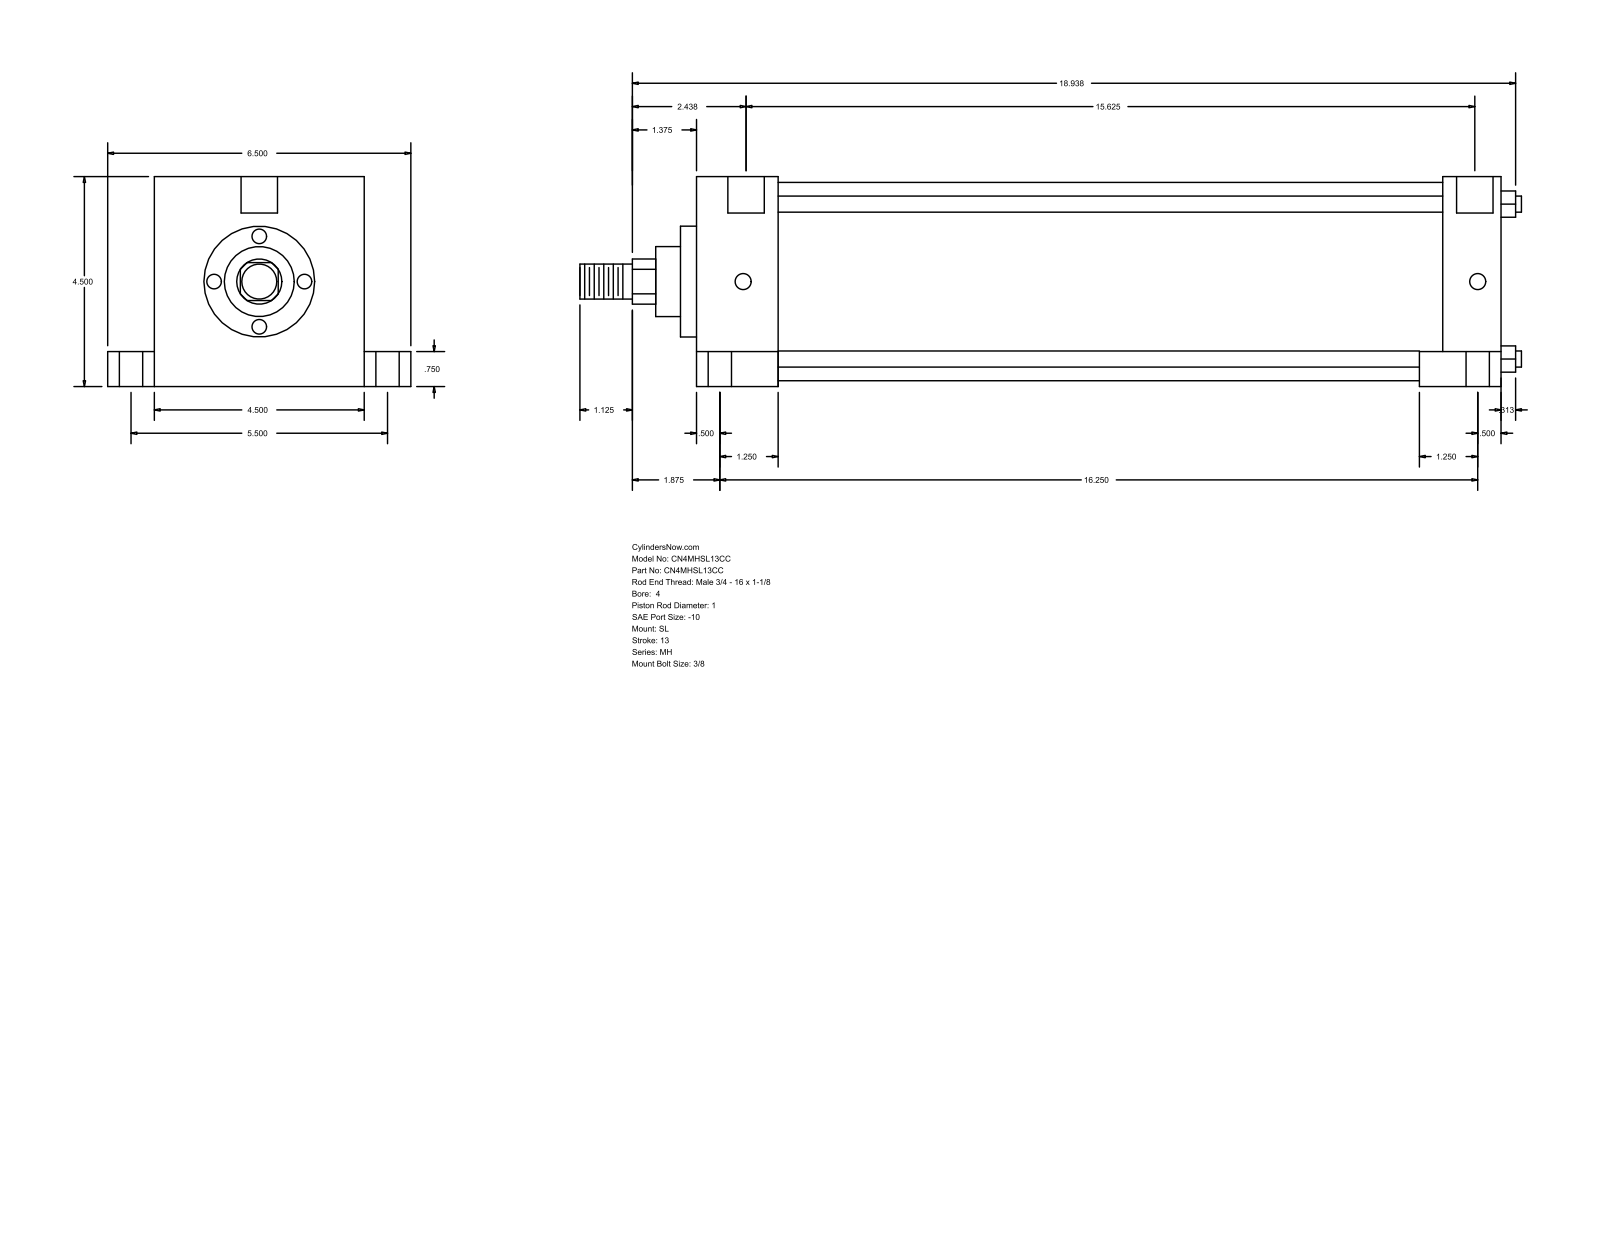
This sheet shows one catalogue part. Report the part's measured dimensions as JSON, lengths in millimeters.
{"part_name": "MH_SL__0400_1", "step_written_by": "GSSL Pune (CONFIG_CONTROL_DESIGN)", "units": "millimeters", "bodies": {"solids": 0, "faces": 110, "planar": 77, "cylindrical": 33, "other": 0}, "overall_size": [512.76, 165.1, 114.3], "round_holes": [[8.73, 4], [12.7, 4], [19.05, 4], [19.84, 2]], "round_bosses_or_shafts": [[8.76, 4], [107.95, 1], [60.33, 1], [38.1, 1], [25.4, 1], [19.05, 1]], "partial_cylinders_radius": [[12.29, 1]], "face_to_face_distances": [114.3, 438.15, 44.46, 393.69, 406.4, 361.94, 31.75, 25.4, 139.7, 19.05], "hole_center_spacings": [69.85, 69.87, 71, 71.3, 139.7, 400.05, 404.55, 406.1]}
